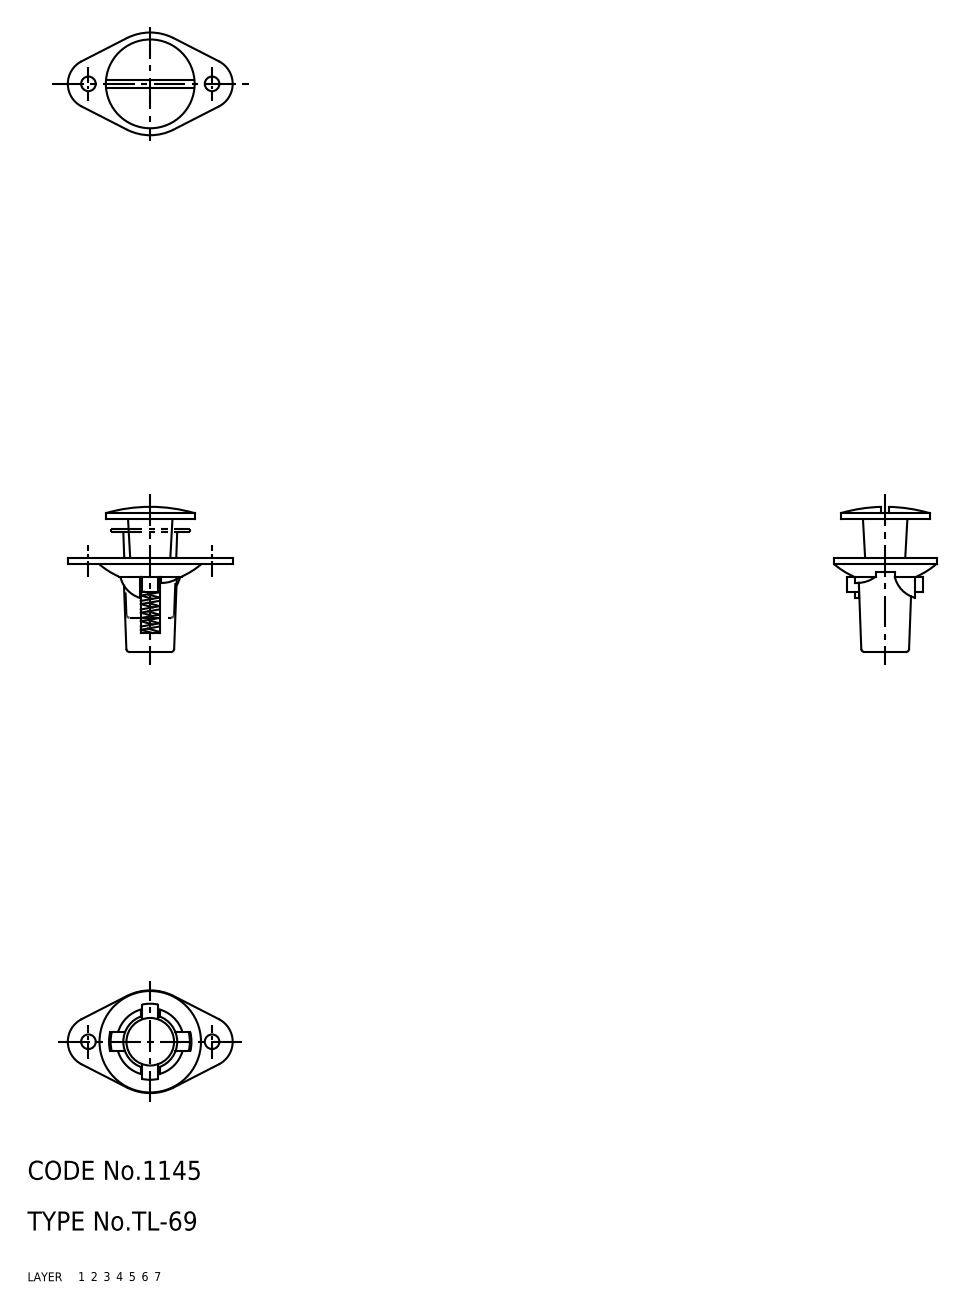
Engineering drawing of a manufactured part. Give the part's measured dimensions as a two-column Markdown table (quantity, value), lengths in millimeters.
| quantity | value |
| --- | --- |
| part name | spring; housing; fastener; base (+1 more) |
| STEP written by | CADfix (AUTOMOTIVE_DESIGN) |
| units | millimeters |
| bodies | 4 solids, 104 faces (0 planar, 0 cylindrical, 104 other) |
| overall size | 26 × 22.89 × 16.2 |
| volume | 1 120 mm³ |
| surface area | 2 435 mm² |
